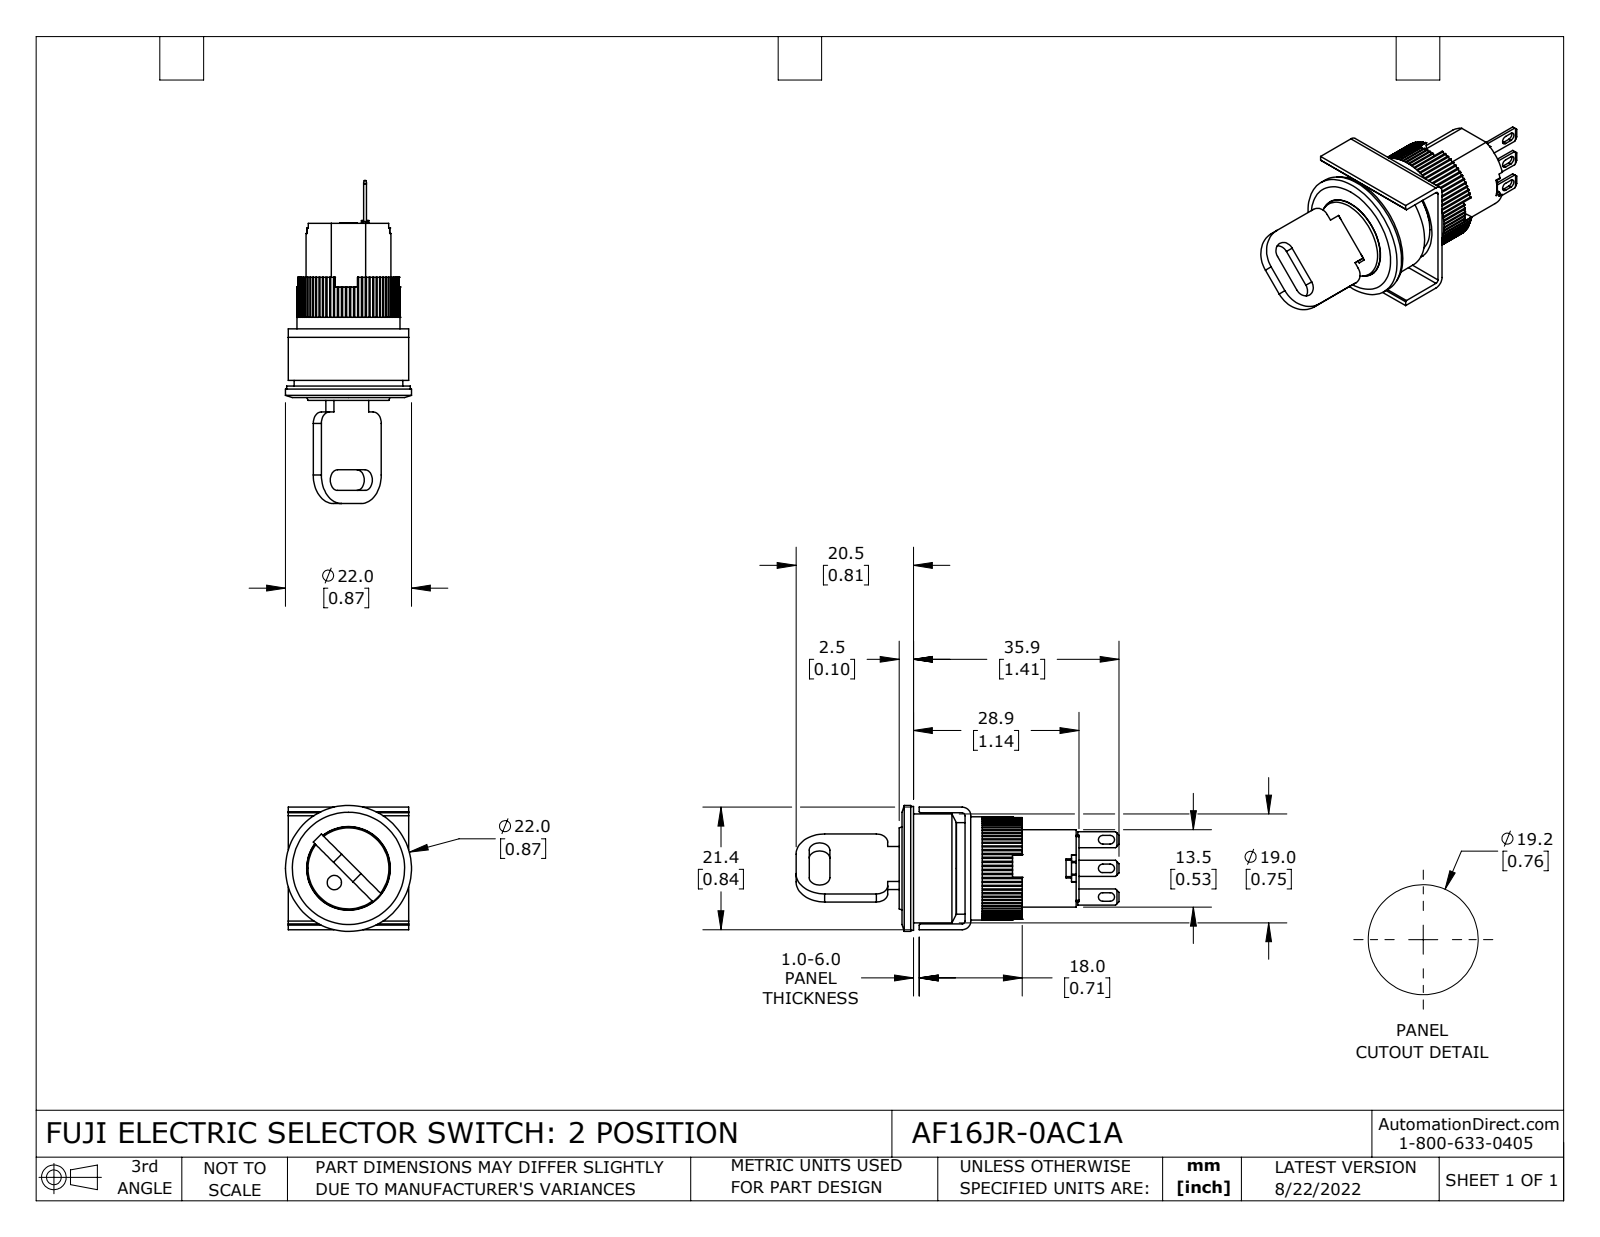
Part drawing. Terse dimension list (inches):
name: AF16JR-0AC1A
written by: SolidWorks 2021 (CONFIG_CONTROL_DESIGN)
unit: in
bodies: 10 solids, 639 faces (456 planar, 177 cylindrical, 6 other)
size: 2.22 × 0.866 × 0.866
volume: 0.493 in³; area: 11.01 in²
holes: 1× ⌀0.039, 1× ⌀0.098, 1× ⌀0.575, 1× ⌀0.709, 1× ⌀0.748
bosses: 1× ⌀0.866, 1× ⌀0.85, 1× ⌀0.63, 1× ⌀0.583, 1× ⌀0.571
rounds: 80× R0.01, 12× R0.008, 6× R0.03, 2× R0.02, 2× R0.059, 2× R0.071, 2× R0.079, 2× R0.197
face distances: 0.079, 0.039, 0.02, 0.374, 0.177, 0.394, 0.803, 0.098, 0.059, 0.764
hole spacings: 0.137
